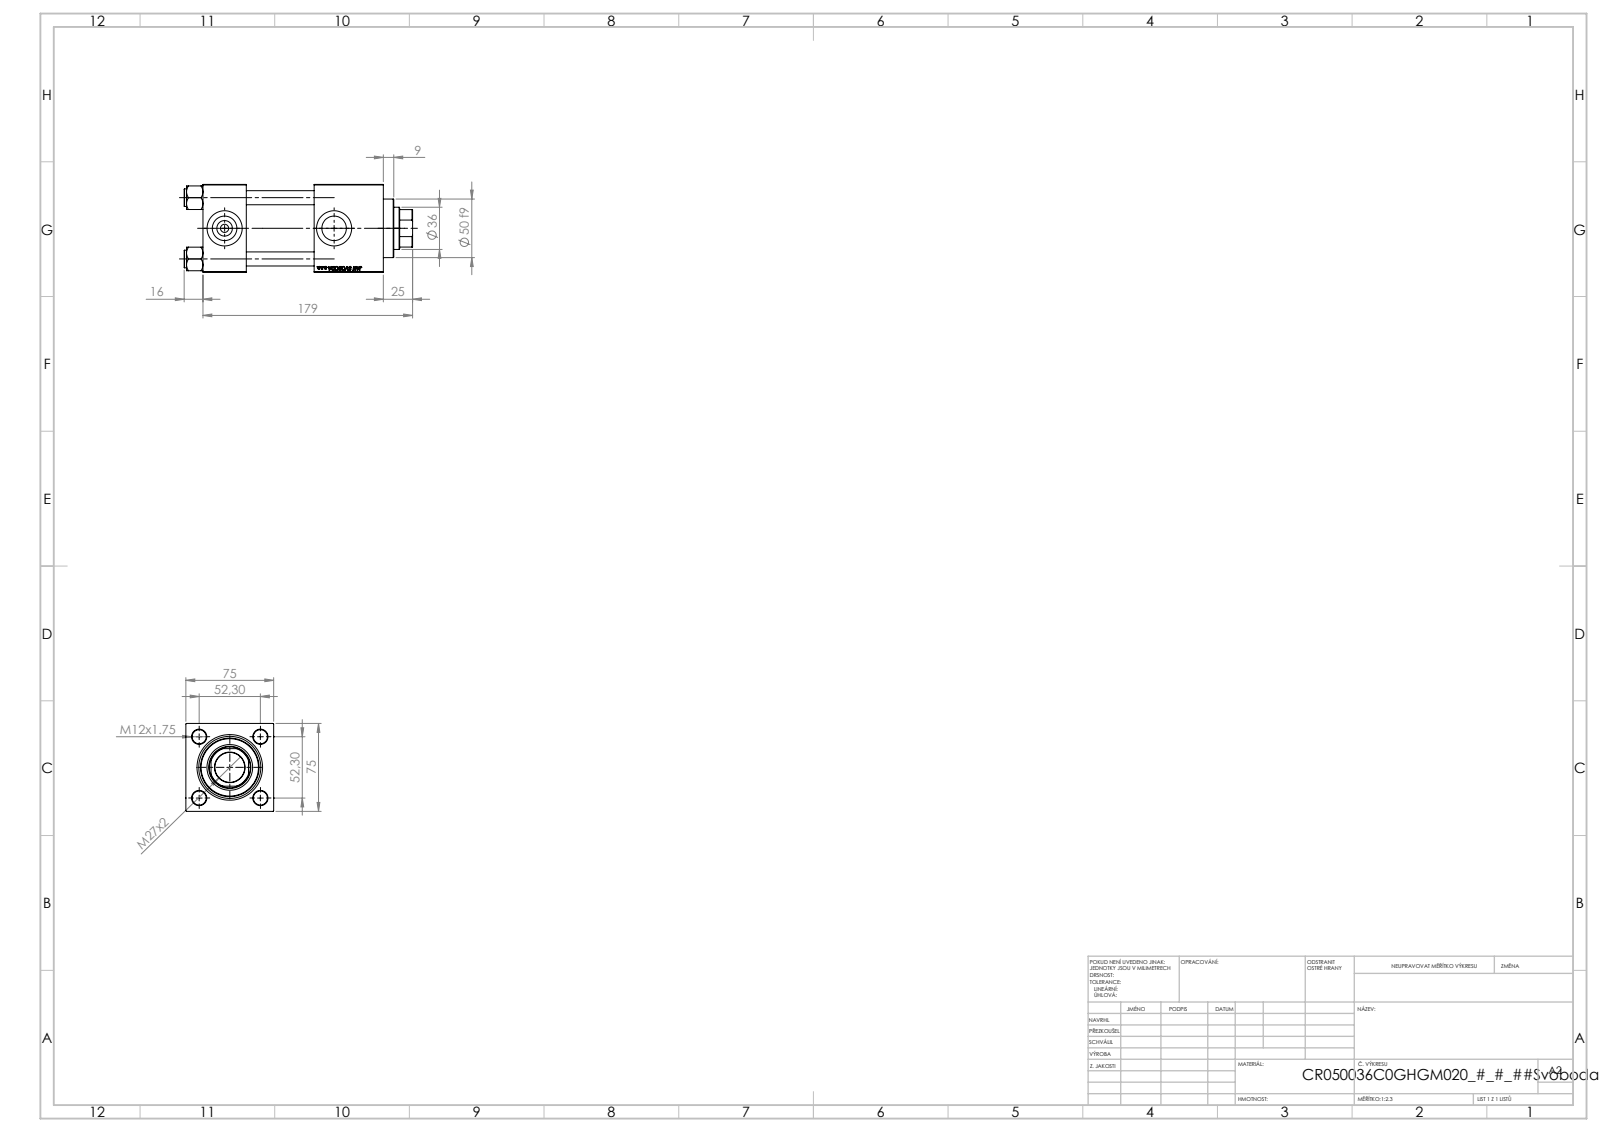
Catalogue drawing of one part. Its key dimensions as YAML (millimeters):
part_name: "V215CR_C_TYCINKA; V215_VC_A; V215CR_VCP_C; NUT_M5_C (+1 more)"
step_written_by: "SolidWorks 2019 (CONFIG_CONTROL_DESIGN)"
units: millimeters
bodies: {solids: 11, faces: 1148, planar: 526, cylindrical: 86, other: 536}
overall_size: [195, 75.54, 75]
volume: 686044
surface_area: 155490
round_holes:
  - {diameter: 12, count: 4}
  - {diameter: 7, count: 2}
  - {diameter: 20.96, count: 2}
  - {diameter: 30, count: 2}
  - {diameter: 25.5, count: 1}
  - {diameter: 36, count: 1}
  - {diameter: 39, count: 1}
  - {diameter: 41, count: 1}
  - {diameter: 53, count: 1}
round_bosses_or_shafts:
  - {diameter: 15, count: 4}
  - {diameter: 56, count: 1}
  - {diameter: 50, count: 1}
partial_cylinders:
  - {radius: 17.5, count: 1}
face_to_face_distances: [75, 37, 95, 58, 154, 117, 59, 125.3, 88.3, 30.3]
hole_center_spacings: [36.98, 52.3, 73.96, 93.5]
